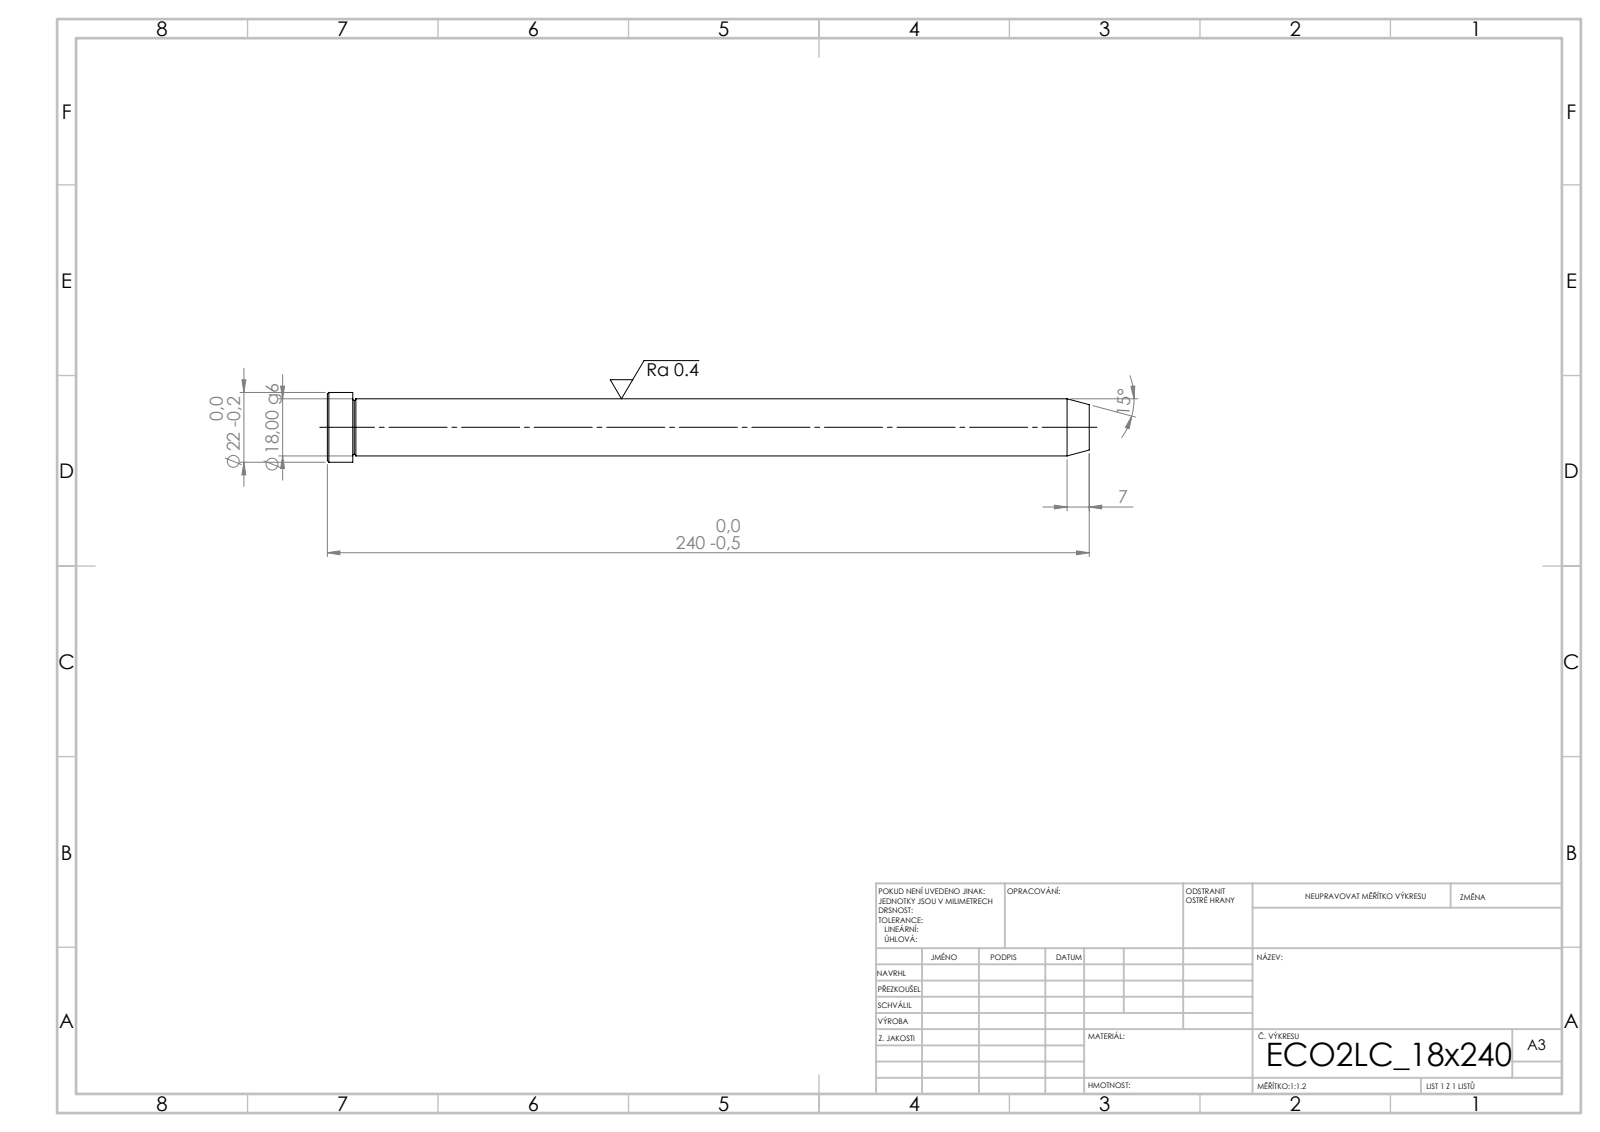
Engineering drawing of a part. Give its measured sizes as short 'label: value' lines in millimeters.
written by: SolidWorks 2019 (CONFIG_CONTROL_DESIGN)
unit: mm
bodies: 1 solid, 15 faces (3 planar, 4 cylindrical, 8 other)
size: 240 × 22 × 22
volume: 61 702 mm³; area: 14 317 mm²
bosses: 1× ⌀22, 1× ⌀18
face distances: 240, 232, 8
